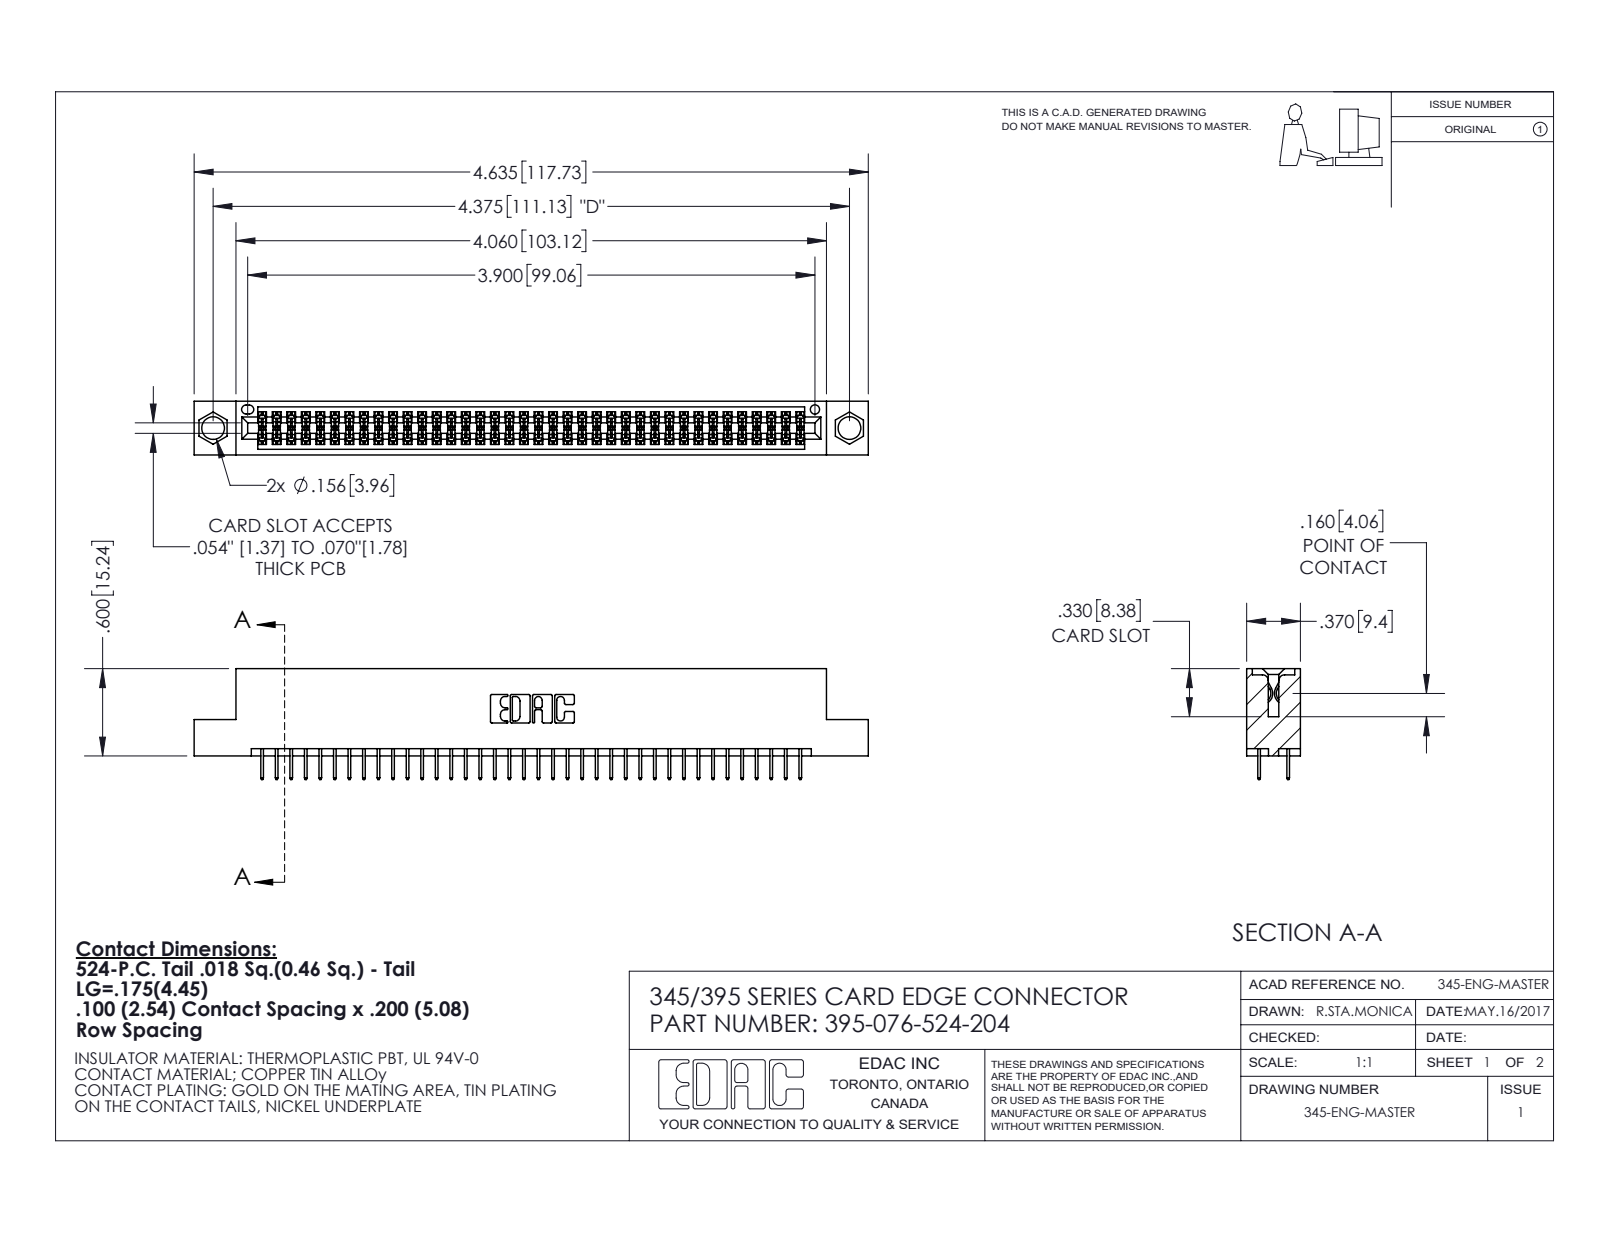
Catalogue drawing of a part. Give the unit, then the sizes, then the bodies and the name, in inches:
Units: inches
Overall size (bounding box): 4.635 × 0.762 × 0.37
Round holes (diameter × count): ⌀0.156 ×2, ⌀0.064 ×1
Partial cylindrical surfaces — rounded edges, fillets, slot ends (radius × count): R0.006 ×114, R0.01 ×22, R0.007 ×6, R0.031 ×6, R0.026 ×3, R0.014 ×2, R0.019 ×2, R0.022 ×2
Main face-to-face distances: 0.072, 0.298, 0.2, 0.37, 0.098, 0.272, 0.025, 0.225, 0.072, 0.175
Hole centre spacings: 0.27, 4.139, 4.375
Volume: 0.682 in³ · Surface area: 24.79 in²
Bodies: 77 solids, 4244 faces (3058 planar, 1186 cylindrical, 0 other)
Part name (STEP PRODUCT): 345-292-001_345-293-124; 345 Part_Flush Mounting Lugs - 0.156 Dia-TI; 395-076-524-204
STEP written by: SolidWorks 2020 (CONFIG_CONTROL_DESIGN)
